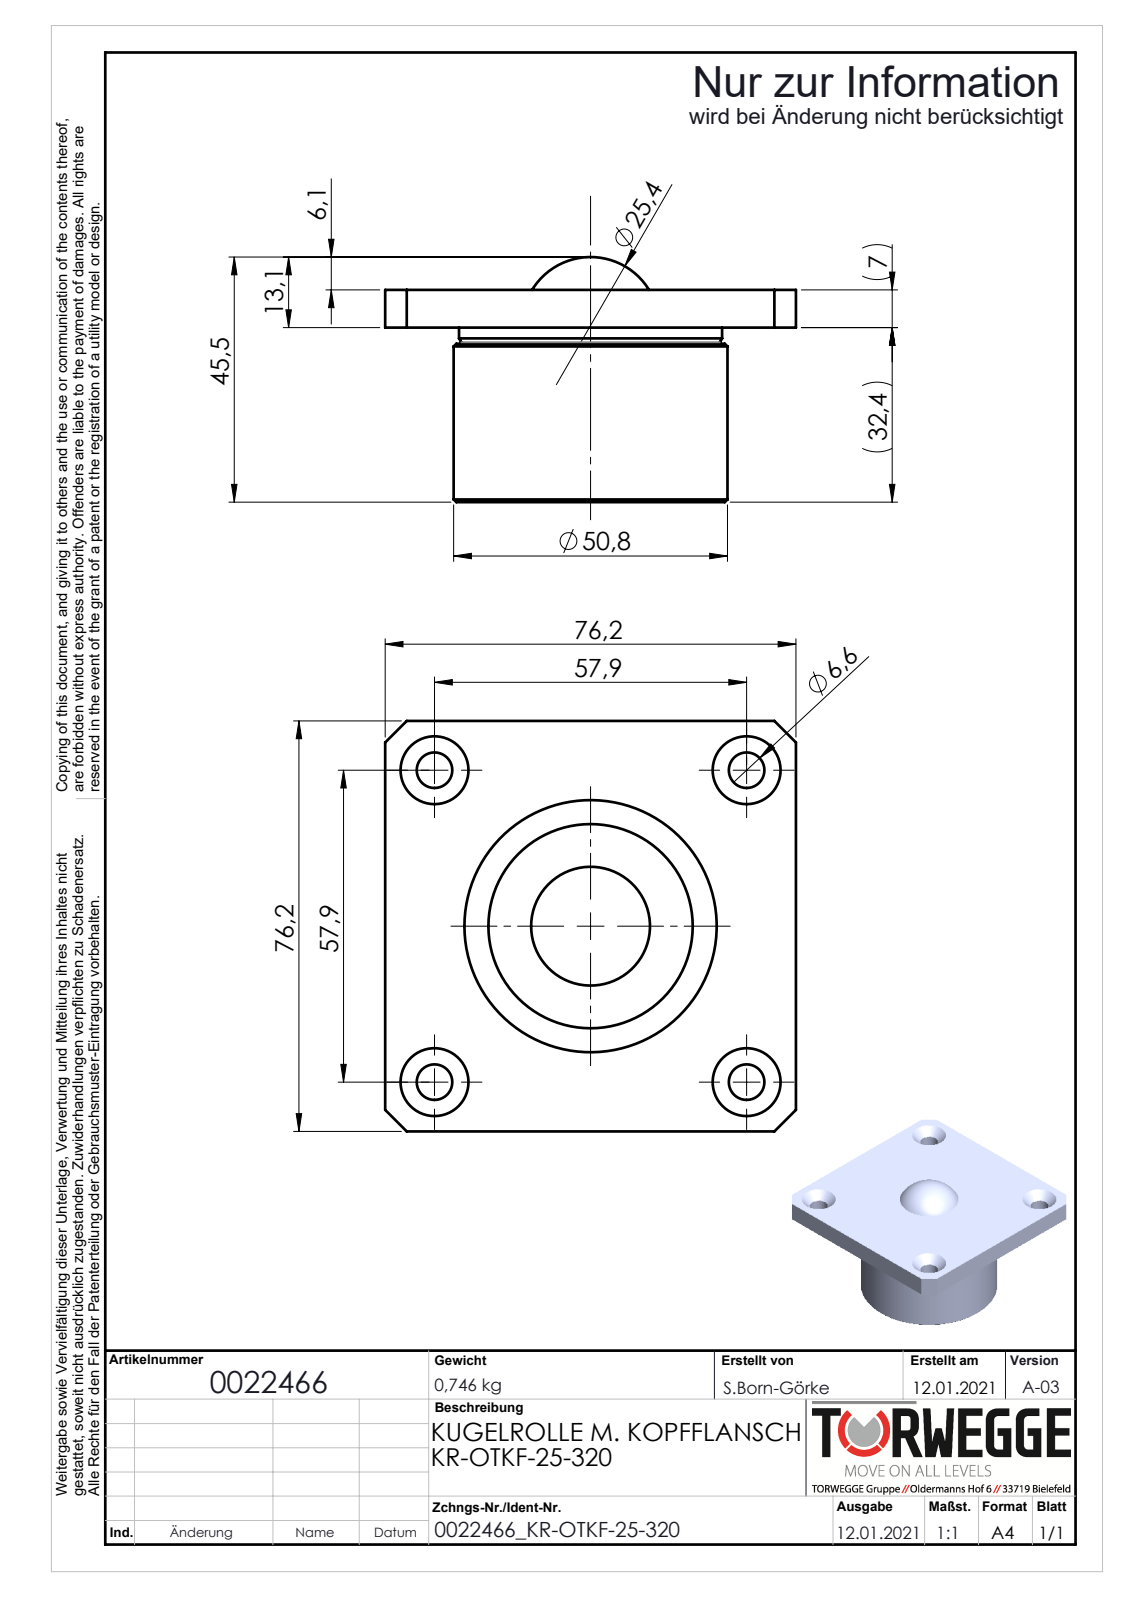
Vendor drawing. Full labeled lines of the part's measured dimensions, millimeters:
Part name (STEP PRODUCT): 0022466
STEP written by: SolidWorks 2018 (AUTOMOTIVE_DESIGN)
Units: millimetres
Bodies: 4 solids, 72 faces (18 planar, 22 cylindrical, 32 other)
Overall size (bounding box): 76.2 × 76.2 × 45.5
Volume: 136 711 mm³ · Surface area: 31 381 mm²
Round holes (diameter × count): ⌀6.6 ×4, ⌀26.1 ×1, ⌀27.5 ×1, ⌀36.3 ×1
Round bosses / shafts (diameter × count): ⌀50.8 ×1, ⌀48.8 ×1, ⌀48 ×1, ⌀38.3 ×1
Main face-to-face distances: 7, 32.4, 39.4, 76.2, 22.01, 10.39, 17.39, 20.4, 1.61, 12
Hole centre spacings: 40.94, 57.9, 81.88
